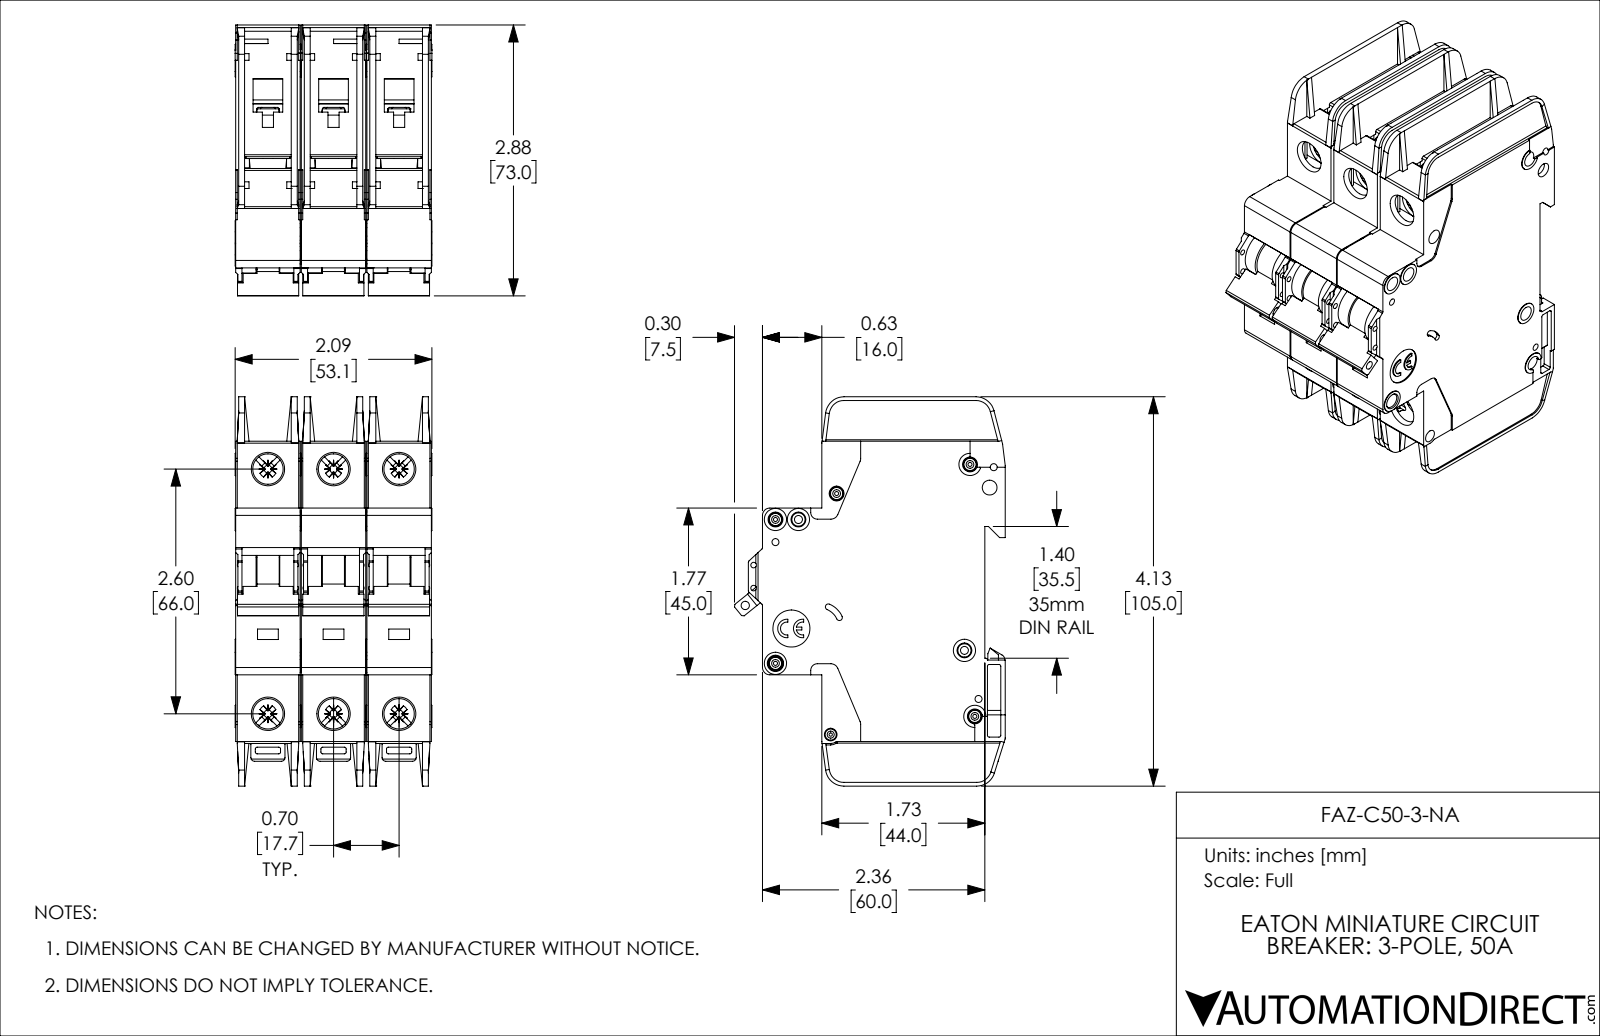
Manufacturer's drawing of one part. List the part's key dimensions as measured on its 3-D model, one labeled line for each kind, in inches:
Part name (STEP PRODUCT): FAZ-C50-3-NA
STEP written by: SolidWorks 2019 (AUTOMOTIVE_DESIGN)
Units: inches
Bodies: 3 solids, 3381 faces (2013 planar, 1071 cylindrical, 297 other)
Overall size (bounding box): 4.134 × 2.876 × 2.091
Volume: 14.05 in³ · Surface area: 123 in²
Round holes (diameter × count): ⌀0.157 ×8, ⌀0.323 ×6, ⌀0.043 ×5, ⌀0.075 ×4, ⌀0.059 ×2, ⌀0.085 ×2, ⌀0.035 ×1, ⌀0.089 ×1, ⌀0.098 ×1, ⌀0.134 ×1, ⌀0.394 ×1
Round bosses / shafts (diameter × count): ⌀0.13 ×5, ⌀0.236 ×4, ⌀0.118 ×4, ⌀0.098 ×3
Partial cylindrical surfaces — rounded edges, fillets, slot ends (radius × count): R0.02 ×72, R0.016 ×30, R0.039 ×18, R0.043 ×12, R0.079 ×12, R0.008 ×6, R0.01 ×6, R0.028 ×6
Main face-to-face distances: 0.697, 0.047, 1.394, 0.685, 0.591, 1.382, 0.744, 0.65, 0.106, 0.094
Hole centre spacings: 0.697, 2.69, 2.598, 0.244, 0.537, 0.87, 1.394, 2.948
